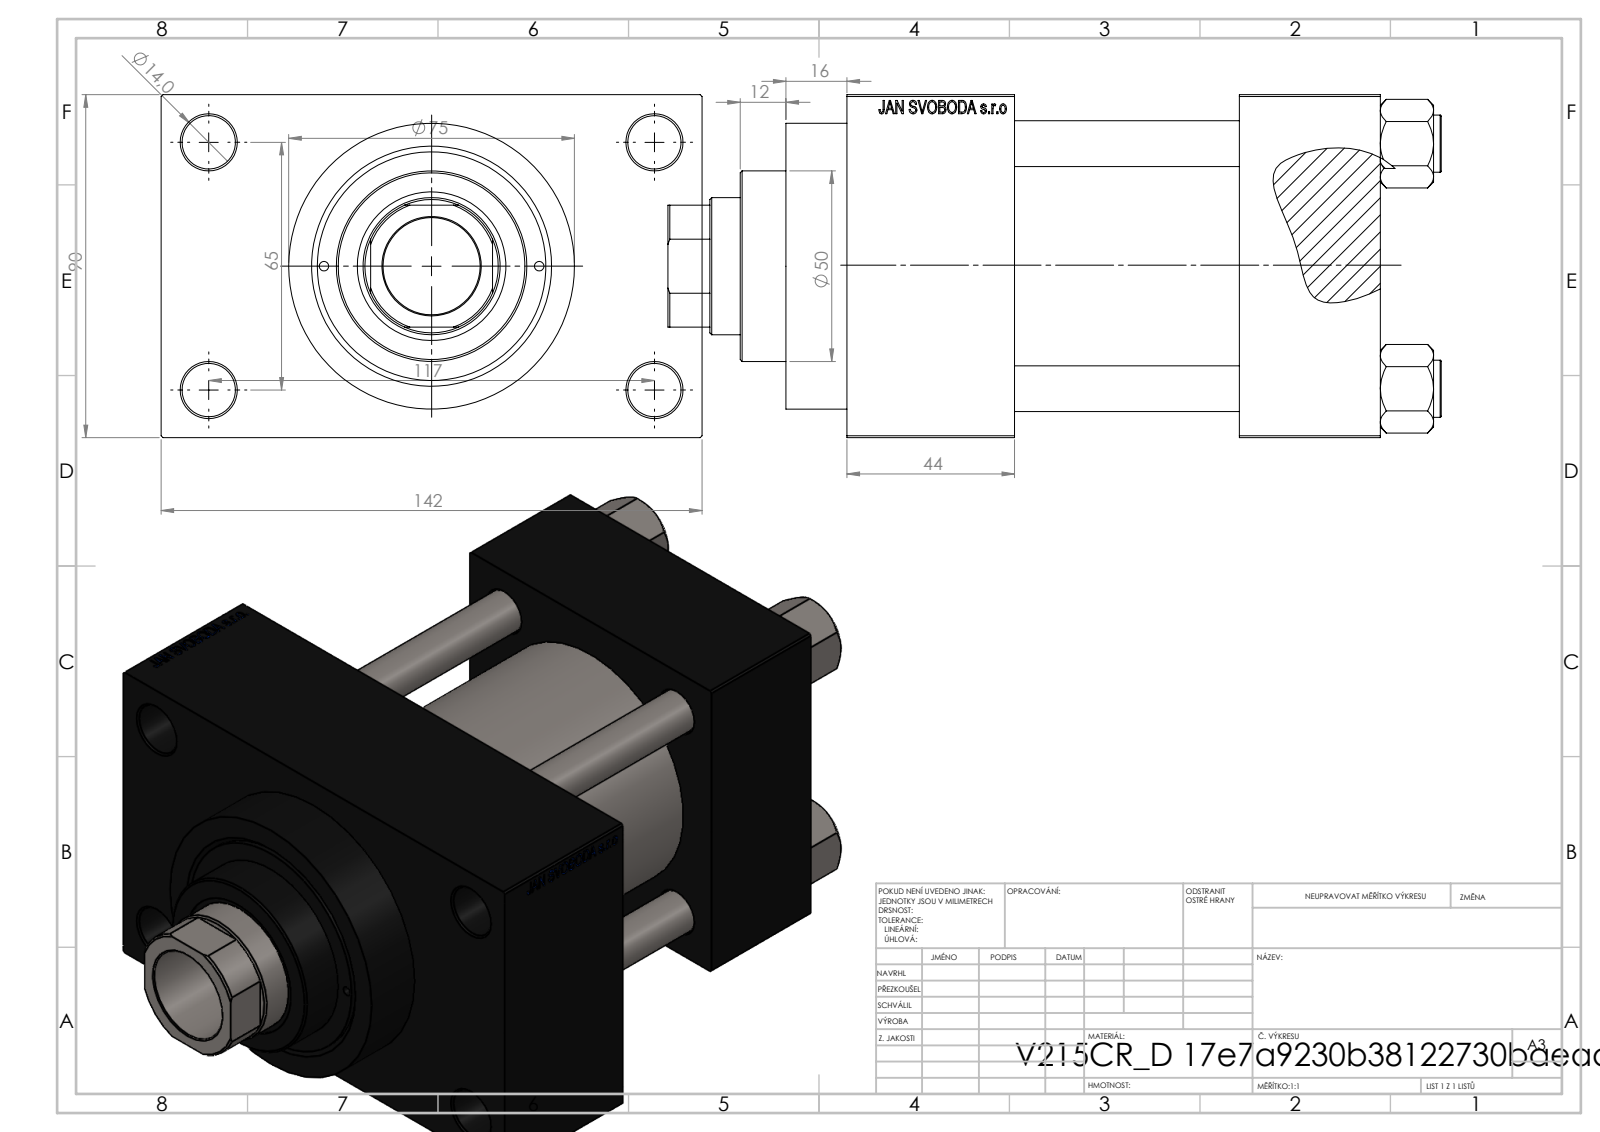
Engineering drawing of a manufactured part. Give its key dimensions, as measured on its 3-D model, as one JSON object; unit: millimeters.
{"part_name": "V215CR_VCP_D; V215CR_D_TYCINKA; NUT_M5_D; V215CR_D_Body (+1 more)", "step_written_by": "SolidWorks 2019 (CONFIG_CONTROL_DESIGN)", "units": "millimeters", "bodies": {"solids": 11, "faces": 1111, "planar": 499, "cylindrical": 92, "other": 520}, "overall_size": [203, 142, 90], "volume_mm3": 1111000, "surface_area_mm2": 205700, "round_holes": [[12, 4], [14, 4], [2.5, 2], [7, 2], [20.96, 2], [30, 2], [25.5, 1], [36, 1], [39, 1], [50, 1], [60, 1], [63, 1]], "round_bosses_or_shafts": [[15, 4], [75, 1], [69, 1]], "partial_cylinders_radius": [[17.5, 1]], "face_to_face_distances": [90, 59, 37, 96, 140, 103, 44, 26, 116, 142], "hole_center_spacings": [26.35, 32.39, 44.4, 45.47, 64.3, 66.92, 68.42, 69.81]}
